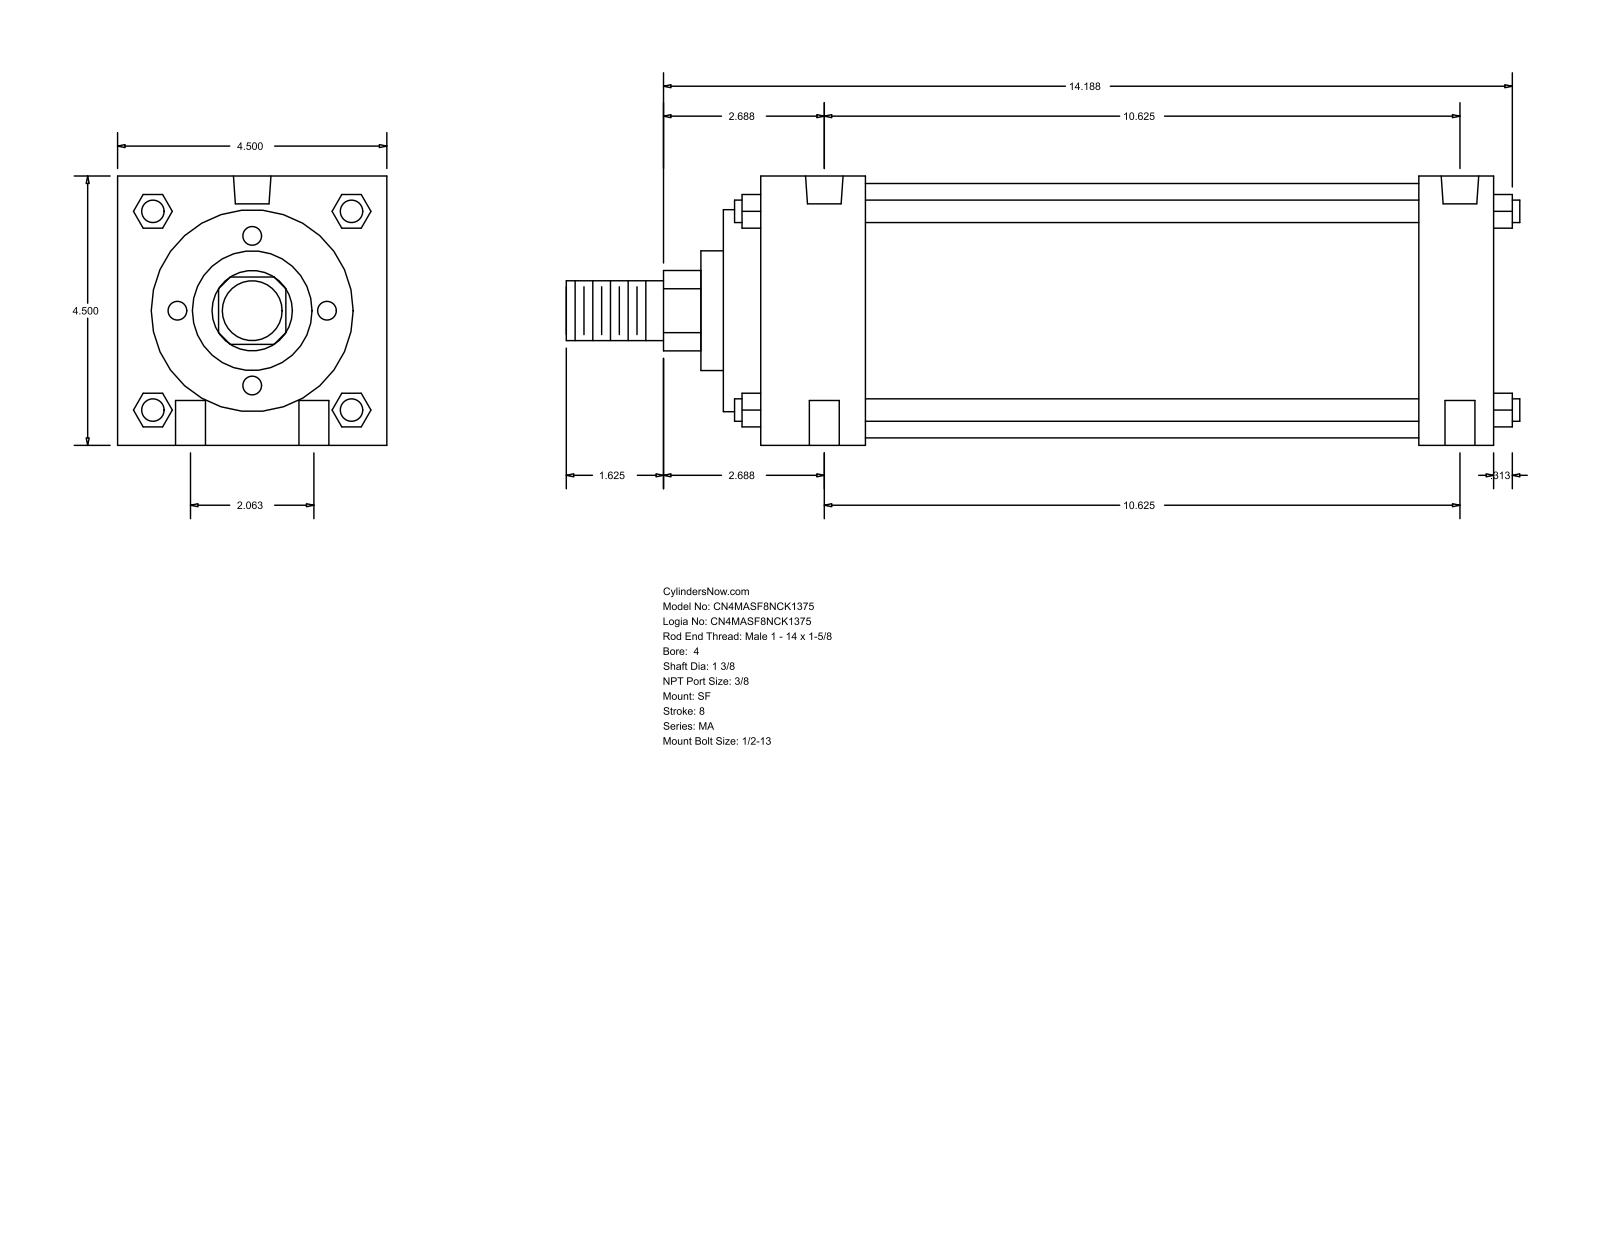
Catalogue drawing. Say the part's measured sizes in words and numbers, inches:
The part is named "MA_SF__0400_1.375". Its 3-D file was written by "GSSL Pune (CONFIG_CONTROL_DESIGN)". It is 0 solids with 126 faces: 95 planar, 31 cylindrical and 0 other. Overall it measures 15.937 by 4.5 by 4.5 inches. Round holes: 4 of diameter 0.5, 2 of diameter 0.437, 2 of diameter 0.627. Round bosses or shafts: 4 of diameter 0.375, 1 of diameter 4.25, 1 of diameter 3.375, 1 of diameter 2, 1 of diameter 1.375, 1 of diameter 1. Partial cylindrical surfaces (rounded edges, fillets, slot ends): 1 of radius 0.672. The main face-to-face distances are 4.5, 12.25, 0.625, 12.875, 11.625, 11, 1.25, 2.375, 1.75, 9.25. The hole center spacings are 1.031, 10.675, 10.625, 2.062, 10.824, 10.25.
